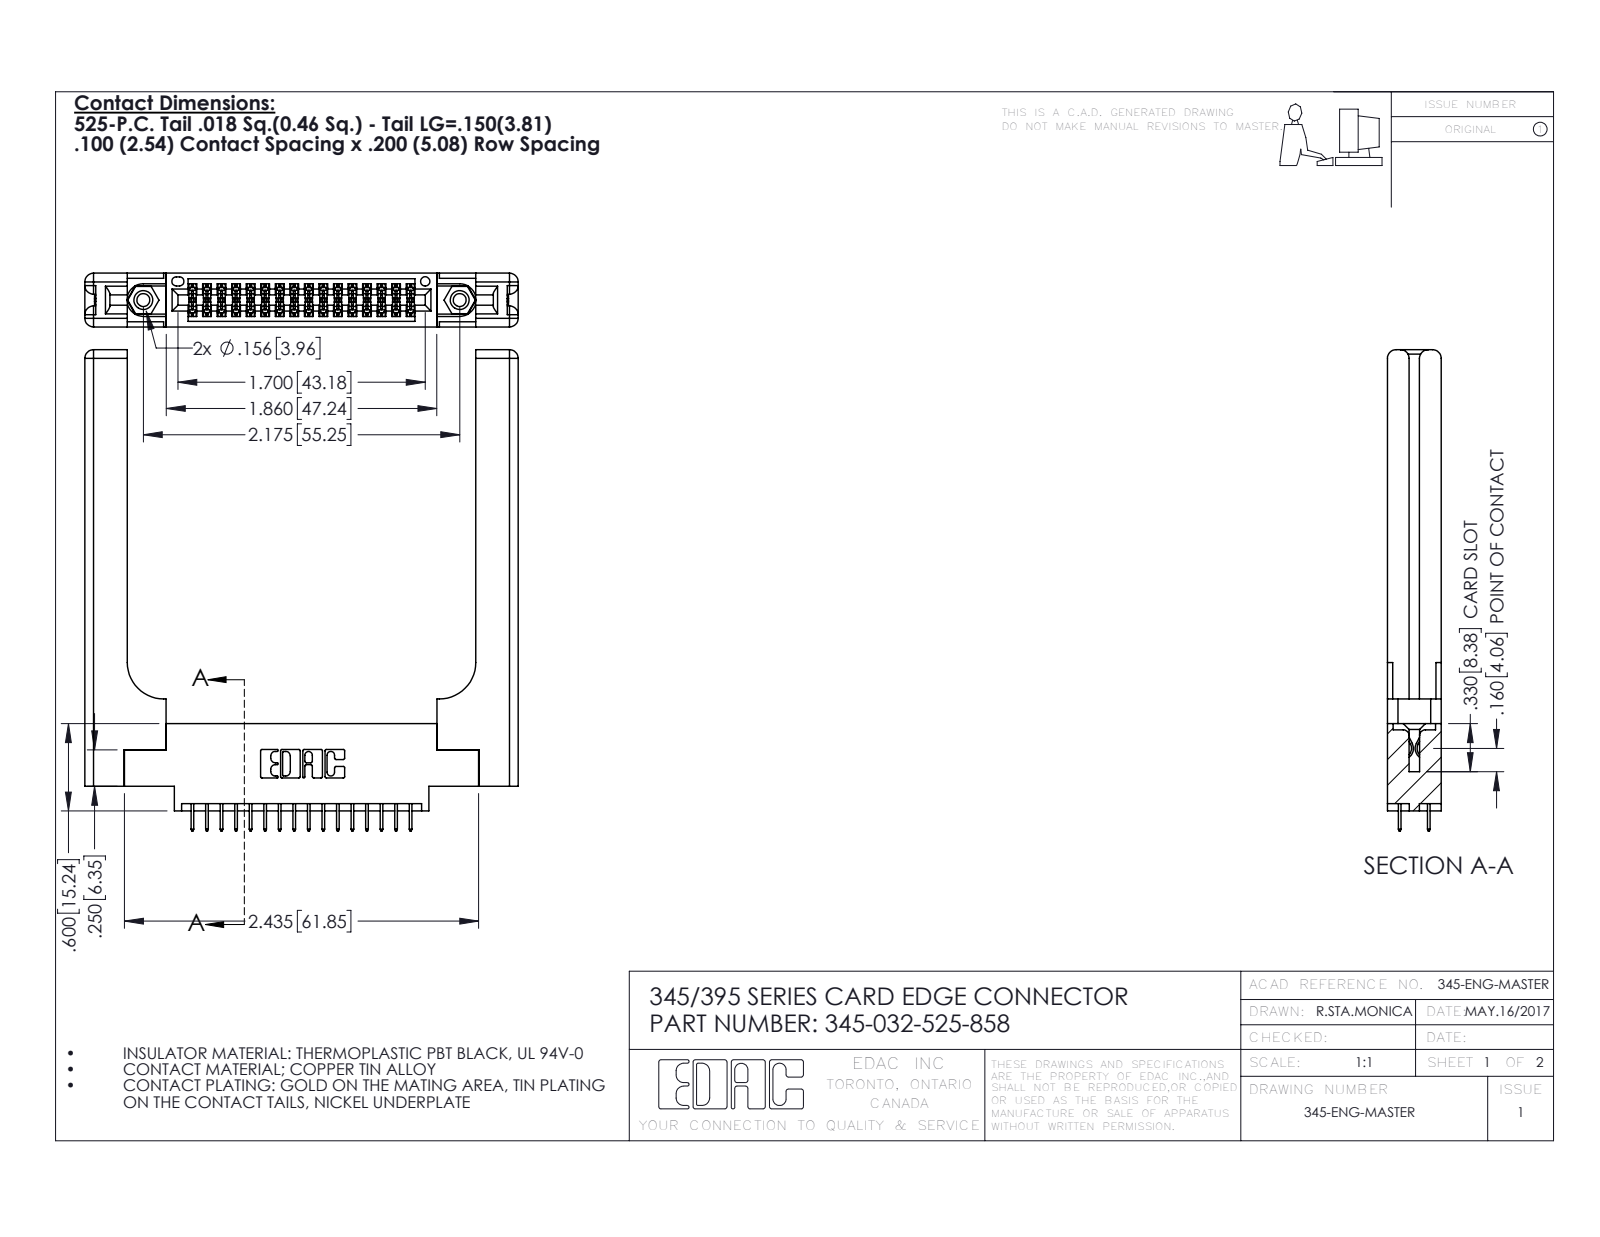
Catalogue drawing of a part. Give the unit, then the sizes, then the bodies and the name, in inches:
Units: inches
Overall size (bounding box): 3.307 × 2.979 × 0.37
Round holes (diameter × count): ⌀0.089 ×2, ⌀0.125 ×2, ⌀0.156 ×2, ⌀0.064 ×1
Round bosses / shafts (diameter × count): ⌀0.155 ×2
Partial cylindrical surfaces — rounded edges, fillets, slot ends (radius × count): R0.006 ×48, R0.01 ×22, R0.06 ×16, R0.007 ×6, R0.031 ×6, R0.026 ×3, R0.014 ×2, R0.019 ×2
Main face-to-face distances: 0.37, 0.072, 0.298, 0.148, 0.15, 0.077, 0.22, 0.225, 0.123, 0.098
Hole centre spacings: 0.27, 1.942, 2.175
Volume: 0.941 in³ · Surface area: 22.94 in²
Bodies: 37 solids, 2114 faces (1480 planar, 574 cylindrical, 60 other)
Part name (STEP PRODUCT): 345-220-058_345-220-058; 345-292-001_345-293-125; 345-032-525-858; 345 Part_0.170 Offset - 0.156 Dia-TH (+1 more)
STEP written by: SolidWorks 2020 (CONFIG_CONTROL_DESIGN)
